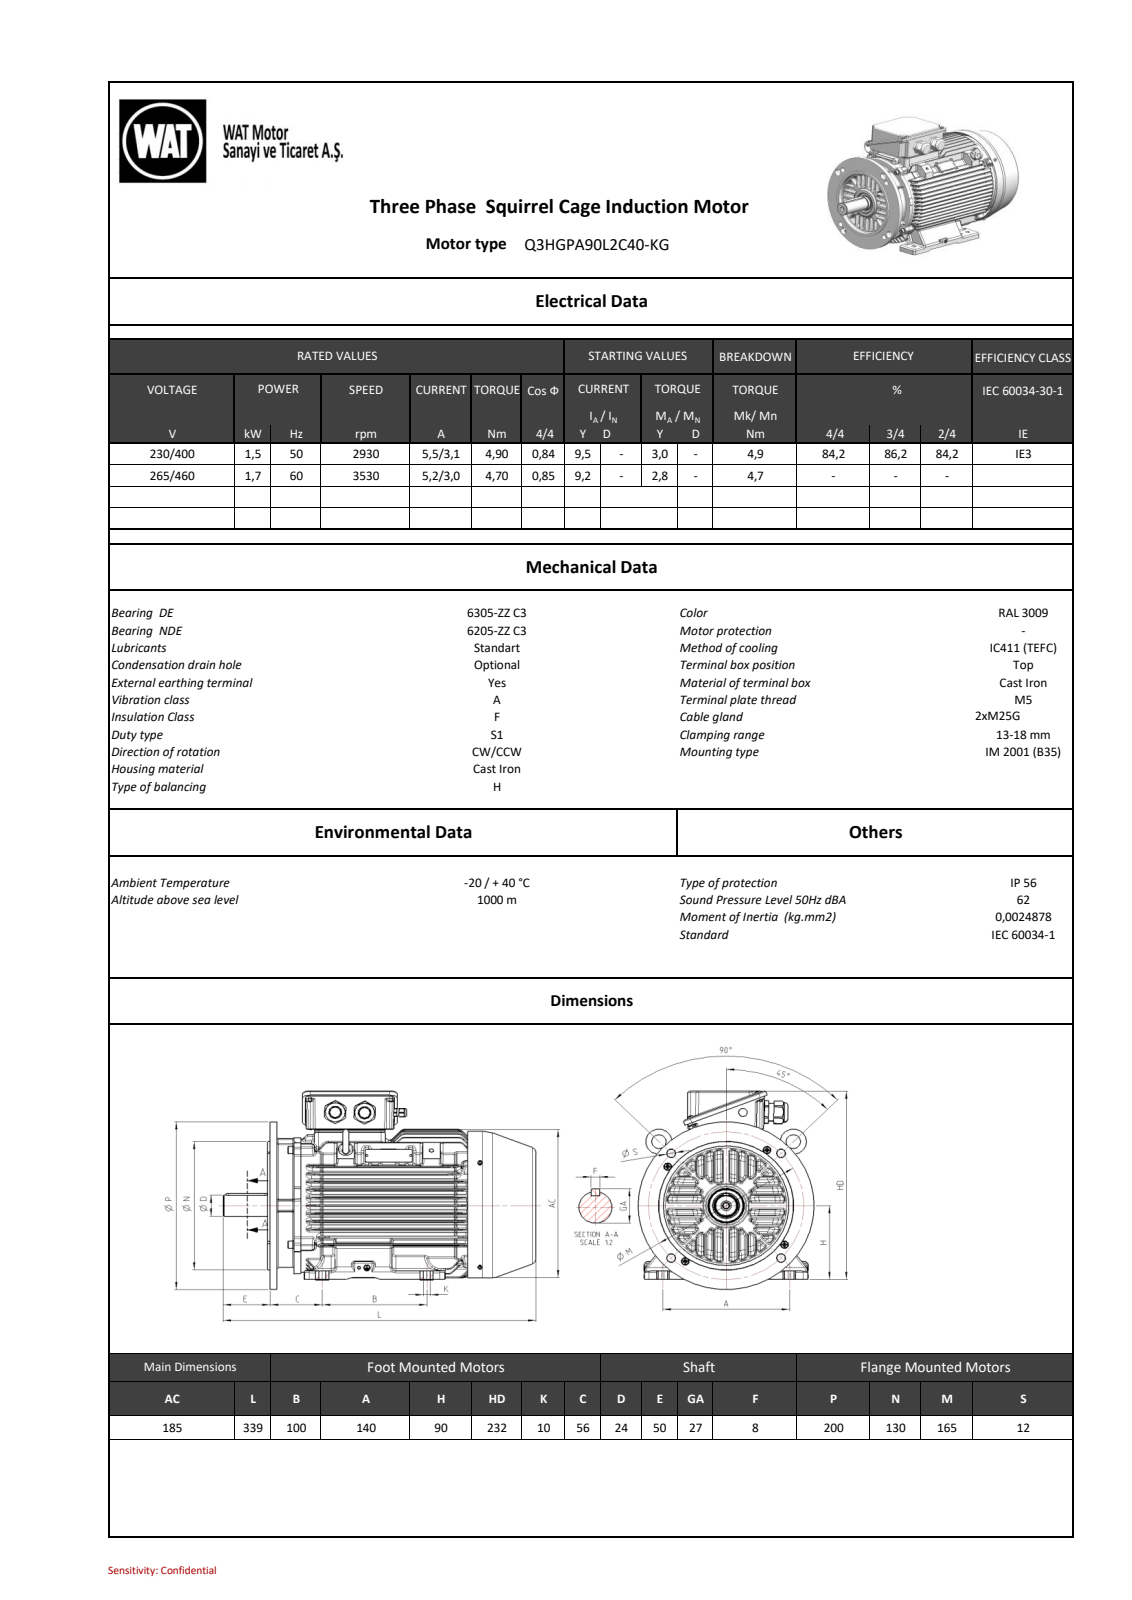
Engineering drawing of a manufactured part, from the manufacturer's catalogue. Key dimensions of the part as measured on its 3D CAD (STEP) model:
Part name (STEP PRODUCT): 26000A30F4D8roc3
STEP written by: SIEMENS PLM Software NX 11.0 (AUTOMOTIVE_DESIGN)
Units: millimetres
Bodies: 0 solids, 3215 faces (885 planar, 904 cylindrical, 1426 other)
Overall size (bounding box): 338.42 × 241.98 × 226.53
Round holes (diameter × count): ⌀10 ×6, ⌀13.5 ×4, ⌀4.2 ×3, ⌀2.5 ×2, ⌀17.2 ×2, ⌀6.5 ×1, ⌀6.8 ×1, ⌀8.4 ×1, ⌀36.9 ×1, ⌀37.1 ×1, ⌀174 ×1
Round bosses / shafts (diameter × count): ⌀20 ×4, ⌀8.65 ×3, ⌀8 ×3, ⌀5 ×3, ⌀27.7 ×2, ⌀25.25 ×2, ⌀200 ×1, ⌀176 ×1
Partial cylindrical surfaces — rounded edges, fillets, slot ends (radius × count): R1.5 ×305, R2 ×52, R1 ×34, R3 ×32, R4 ×32, R5 ×24, R1.2 ×20, R26.5 ×12
Main face-to-face distances: 6.45, 12.04, 232.18, 238.63, 49.79, 281.97, 288.42, 62.58, 3, 3.01
Hole centre spacings: 116.67, 80.5, 139.43, 21.36, 82.5, 99.24, 129.32, 150.59
